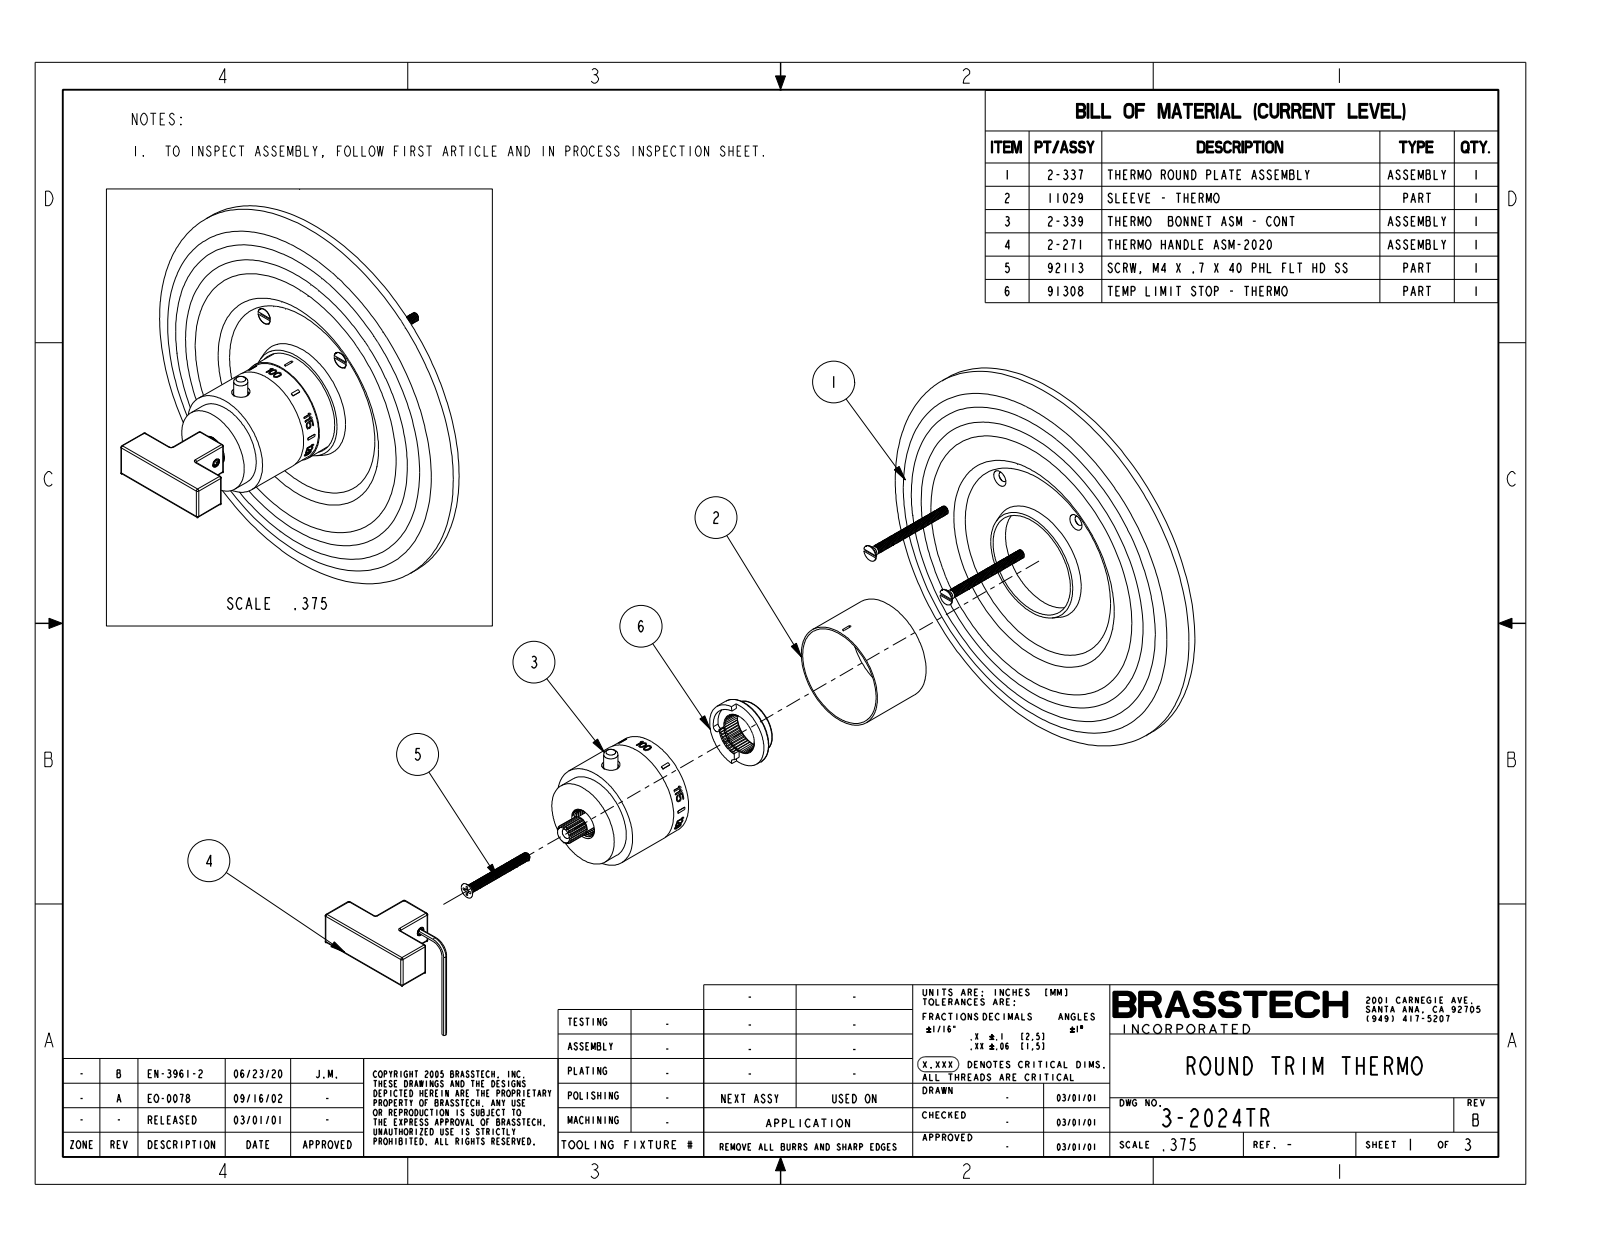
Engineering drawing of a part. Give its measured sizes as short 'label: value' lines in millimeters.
name: 3-2024TR
written by: CREO PARAMETRIC BY PTC INC, 2018400 (CONFIG_CONTROL_DESIGN)
unit: mm
bodies: 1 solid, 431 faces (338 planar, 59 cylindrical, 34 other)
size: 190.5 × 190.5 × 102.2
volume: 418 000 mm³; area: 76 580 mm²
bosses: 1× ⌀190.5, 1× ⌀50, 1× ⌀49.3, 1× ⌀49, 1× ⌀41, 1× ⌀10.2, 1× ⌀6.6, 1× ⌀1.7
rounds: 22× R0.8, 1× R24.6
face distances: 8, 66.6, 58.7, 15.9, 102.2, 94.3, 35.6, 58.7, 50.7, 7.9
